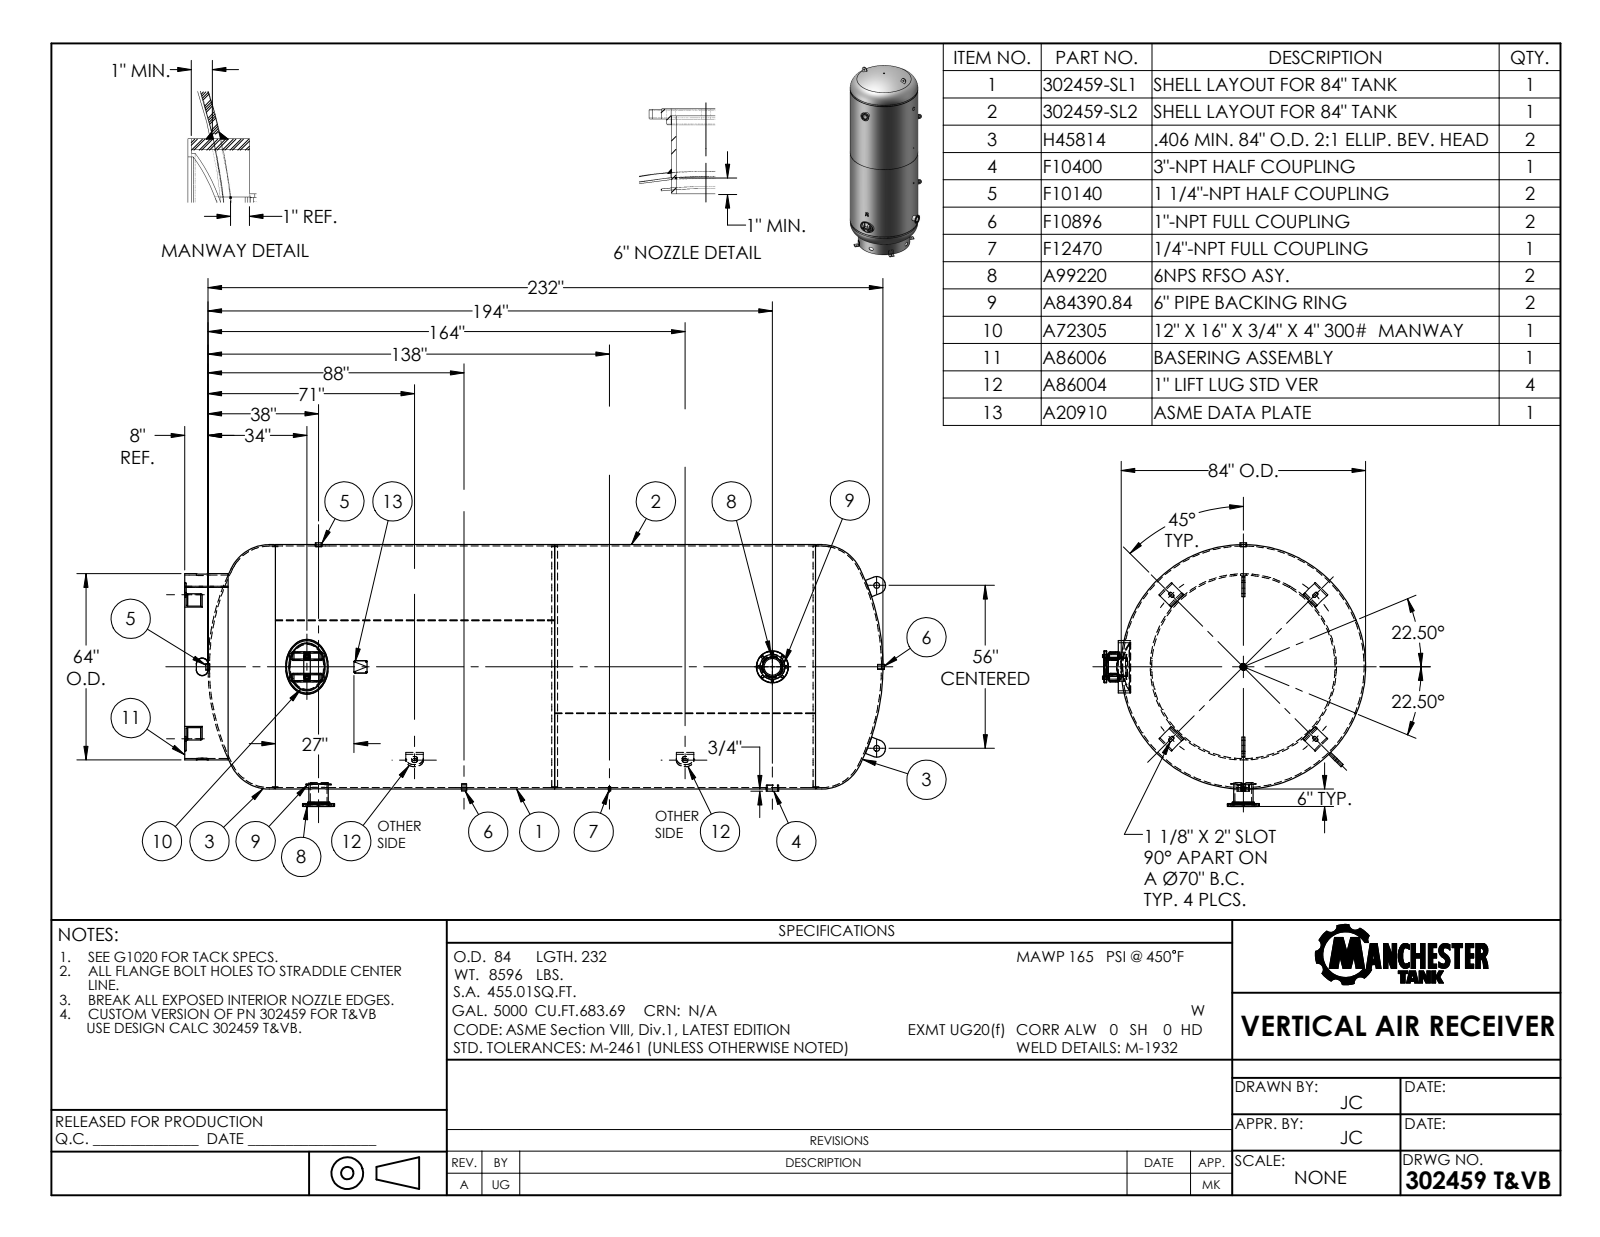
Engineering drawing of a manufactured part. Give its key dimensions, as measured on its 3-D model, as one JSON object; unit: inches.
{"part_name": "302459", "step_written_by": "SolidWorks 2011 (CONFIG_CONTROL_DESIGN)", "units": "inches", "bodies": {"solids": 0, "faces": 337, "planar": 118, "cylindrical": 171, "other": 48}, "overall_size": [240.863, 90.625, 90.371], "round_holes": [[0.875, 16], [2, 4], [1.66, 2], [5.761, 2], [6.72, 2], [1.315, 1], [1.315, 1], [1.875, 1], [2.375, 1], [3.5, 1], [63, 1]], "round_bosses_or_shafts": [[11, 2], [8.5, 2], [6.625, 2], [2.25, 2], [1.75, 2], [1, 2], [84, 1], [83, 1]], "partial_cylinders_radius": [[0.5, 8], [0.563, 8], [0.5, 4], [1.318, 4], [2.937, 4], [2.938, 4], [0.375, 3], [5.917, 1]], "face_to_face_distances": [127.187, 0.5, 96, 31.187, 89.625, 185.625, 216.812, 1, 216.312, 126.687], "hole_center_spacings": [3.635, 4.75, 6.718, 8.777, 8.777, 3.636, 4.75, 6.717]}
